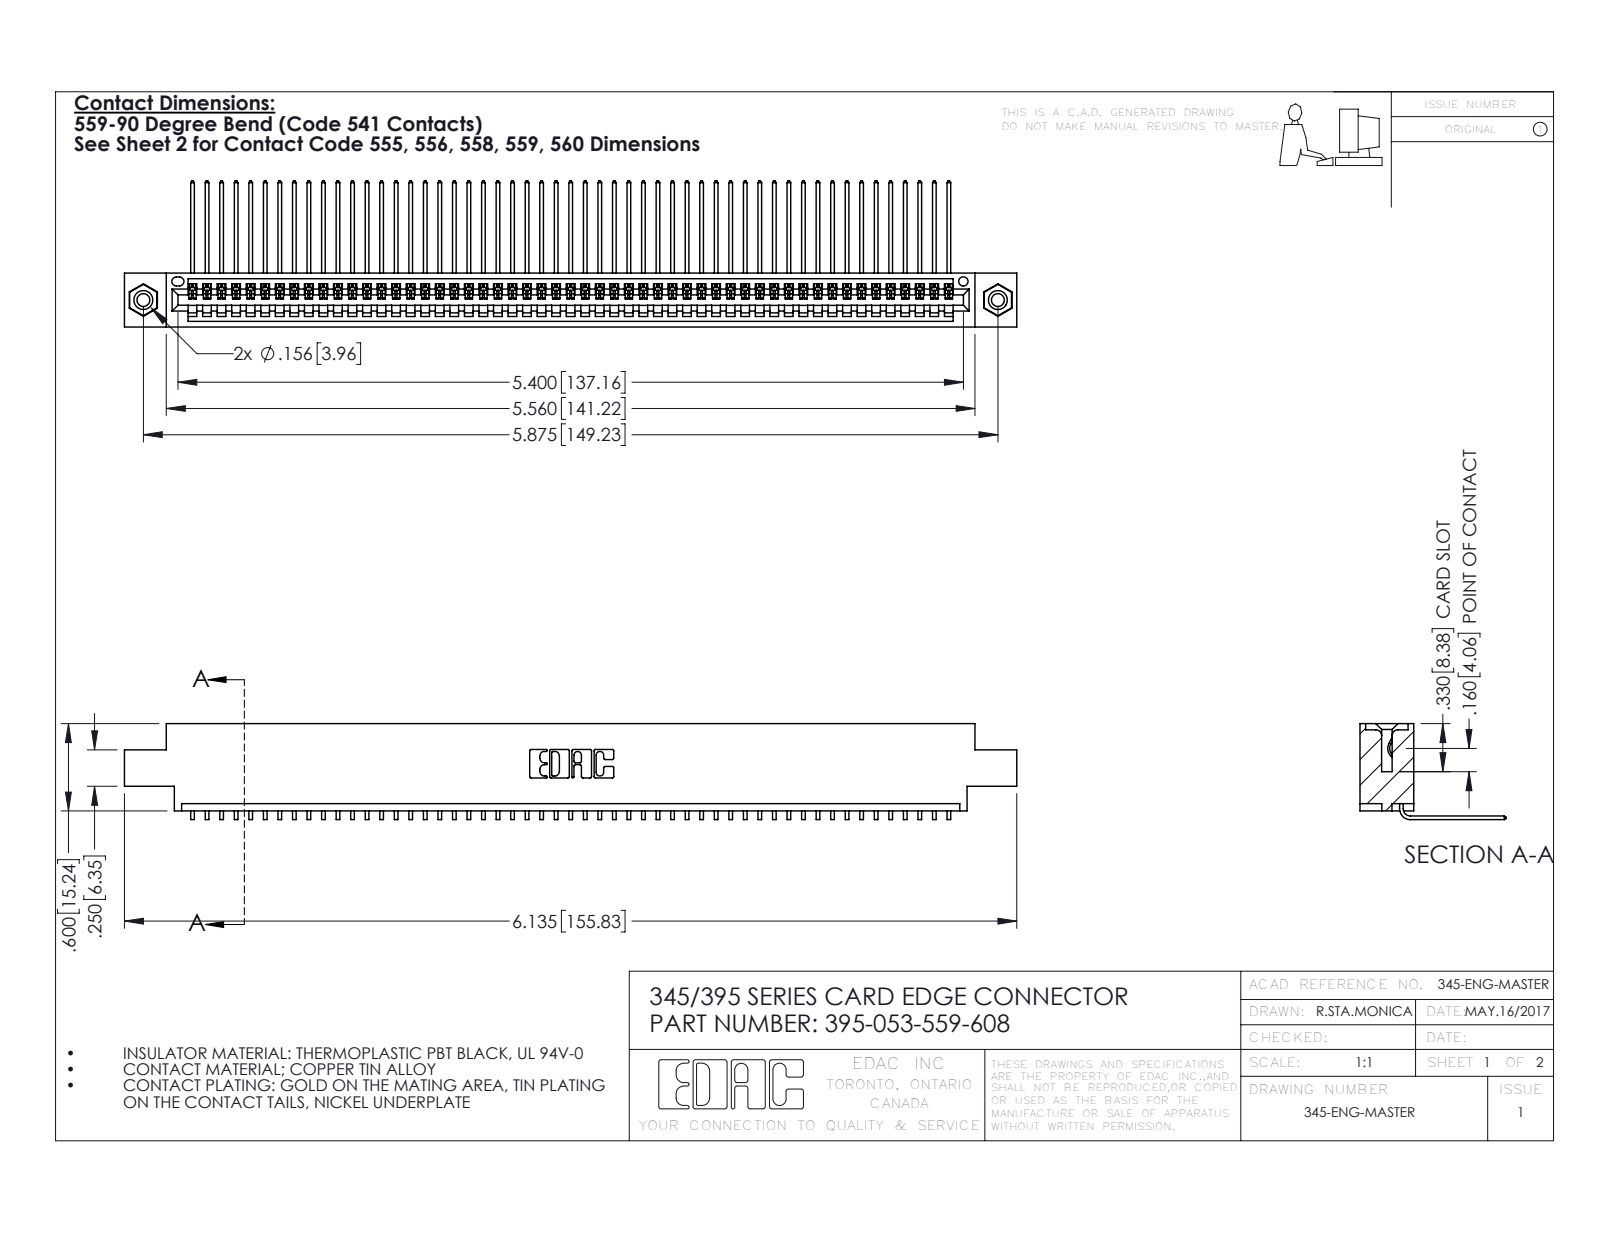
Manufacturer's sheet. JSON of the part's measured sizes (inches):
{"part_name": "395-053-559-608; 345-250-001_345-250-003-102; 345 Part_0.170 Offset - 0.156 Dia-TI; 345-292-001_558 559 Tail - 1", "step_written_by": "SolidWorks 2016 (CONFIG_CONTROL_DESIGN)", "units": "inches", "bodies": {"solids": 56, "faces": 3370, "planar": 2342, "cylindrical": 1012, "other": 16}, "overall_size": [6.135, 1.005, 0.659], "volume_in3": 0.912, "surface_area_in2": 32.86, "round_holes": [[0.089, 2], [0.125, 2], [0.156, 2], [0.064, 1]], "round_bosses_or_shafts": [[0.155, 2]], "partial_cylinders_radius": [[0.006, 106], [0.01, 22], [0.007, 6], [0.031, 6], [0.026, 3], [0.031, 2], [0.04, 2], [0.014, 1]], "face_to_face_distances": [0.072, 0.298, 0.37, 0.2, 0.098, 0.272, 0.025, 0.225, 0.175, 0.149], "hole_center_spacings": [0.27, 5.639, 5.875]}
